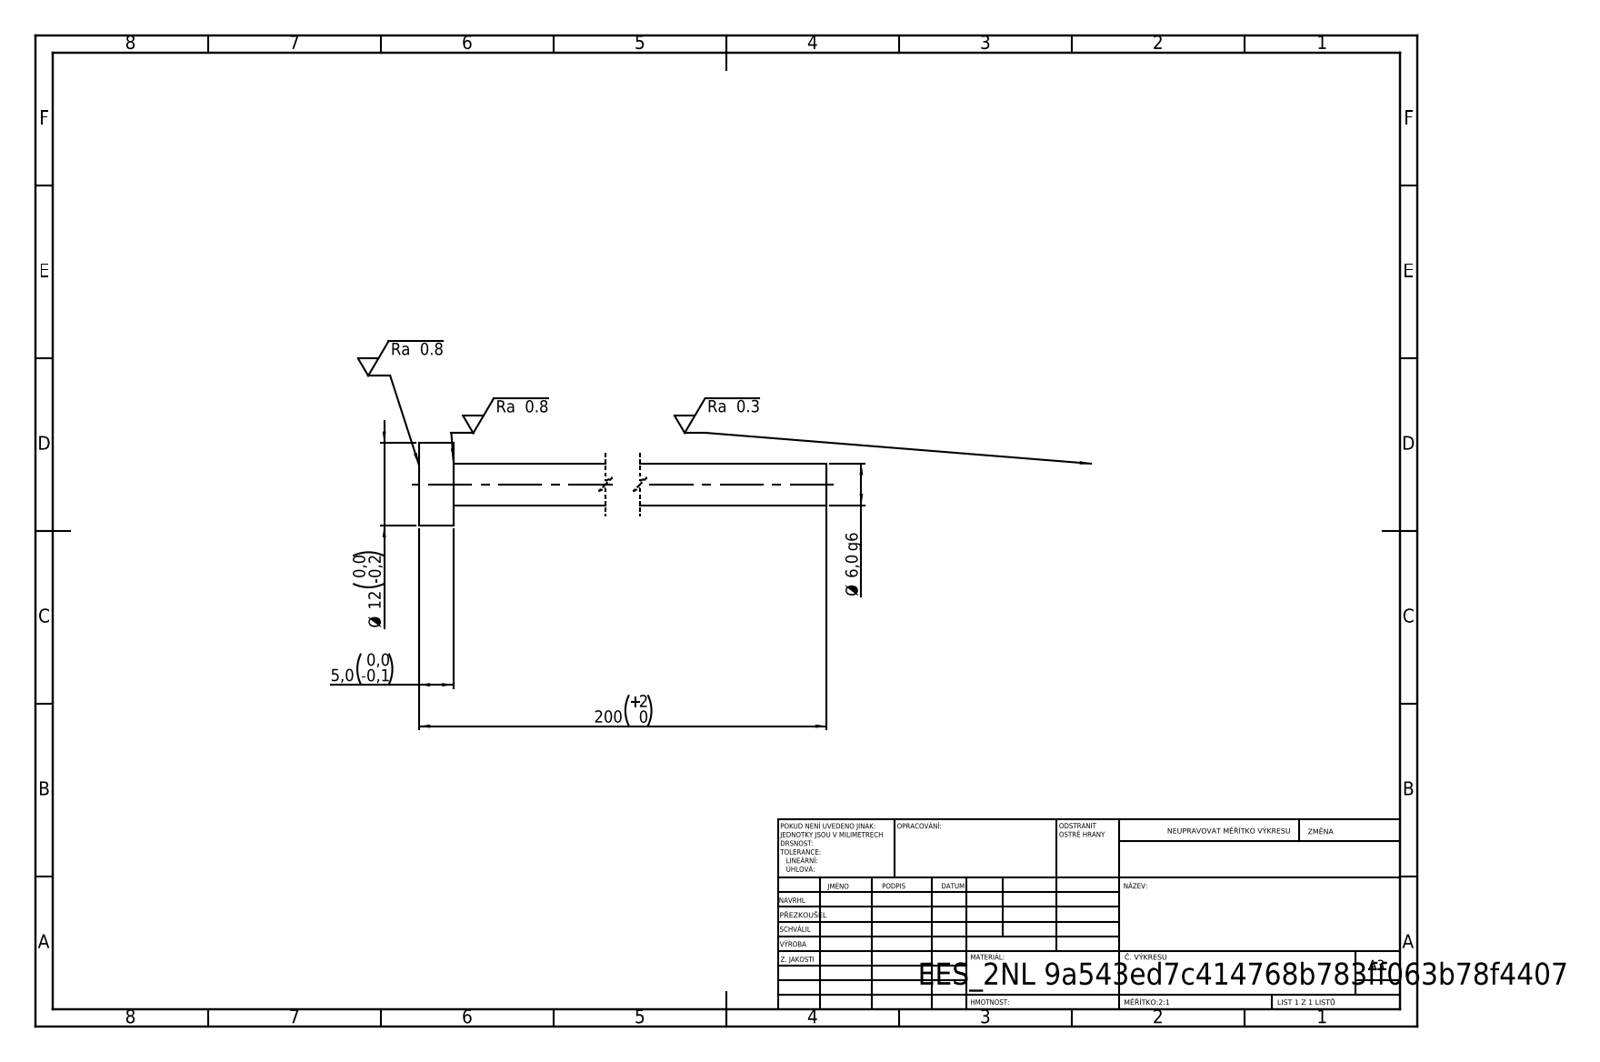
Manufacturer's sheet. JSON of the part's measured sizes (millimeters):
{"step_written_by": "SolidWorks 2019 (CONFIG_CONTROL_DESIGN)", "units": "millimeters", "bodies": {"solids": 1, "faces": 7, "planar": 3, "cylindrical": 4, "other": 0}, "overall_size": [200, 12, 12], "volume_mm3": 6079, "surface_area_mm2": 4090, "round_bosses_or_shafts": [[12, 1], [6, 1]], "face_to_face_distances": [5, 200, 195]}
